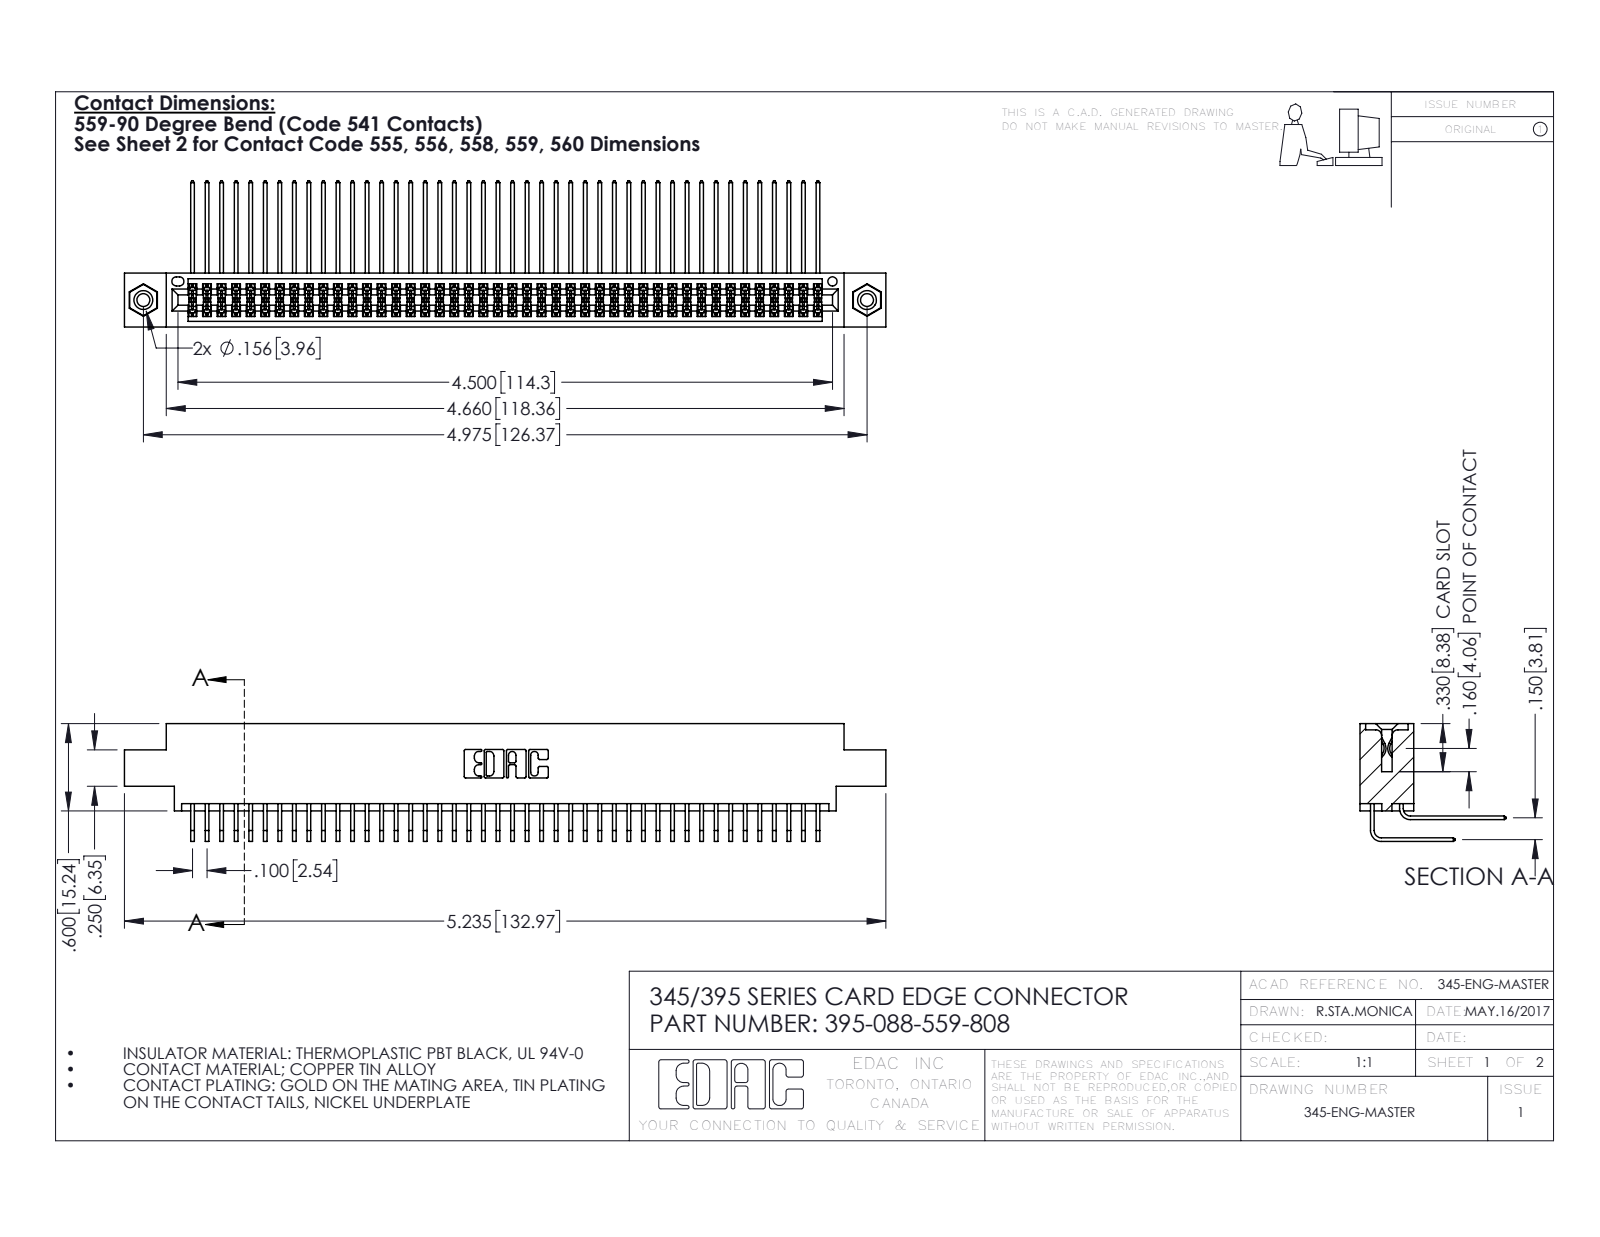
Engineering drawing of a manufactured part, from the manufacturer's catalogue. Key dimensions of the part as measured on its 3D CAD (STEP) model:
Part name (STEP PRODUCT): 345-292-001_558 559 Tail - 1; 345-250-001_345-250-003-102; 395-088-559-808; 345-292-001_559 Tail - 2 (+1 more)
STEP written by: SolidWorks 2016 (CONFIG_CONTROL_DESIGN)
Units: inches
Bodies: 91 solids, 4766 faces (3196 planar, 1554 cylindrical, 16 other)
Overall size (bounding box): 5.235 × 1.005 × 0.809
Volume: 0.813 in³ · Surface area: 34.53 in²
Round holes (diameter × count): ⌀0.089 ×2, ⌀0.125 ×2, ⌀0.156 ×2, ⌀0.064 ×1
Round bosses / shafts (diameter × count): ⌀0.155 ×2
Partial cylindrical surfaces — rounded edges, fillets, slot ends (radius × count): R0.006 ×133, R0.01 ×22, R0.007 ×6, R0.031 ×6, R0.026 ×3, R0.014 ×2, R0.019 ×2, R0.022 ×2
Main face-to-face distances: 0.072, 0.298, 0.37, 0.2, 0.098, 0.272, 0.025, 0.225, 0.175, 0.15
Hole centre spacings: 0.27, 4.739, 4.975
